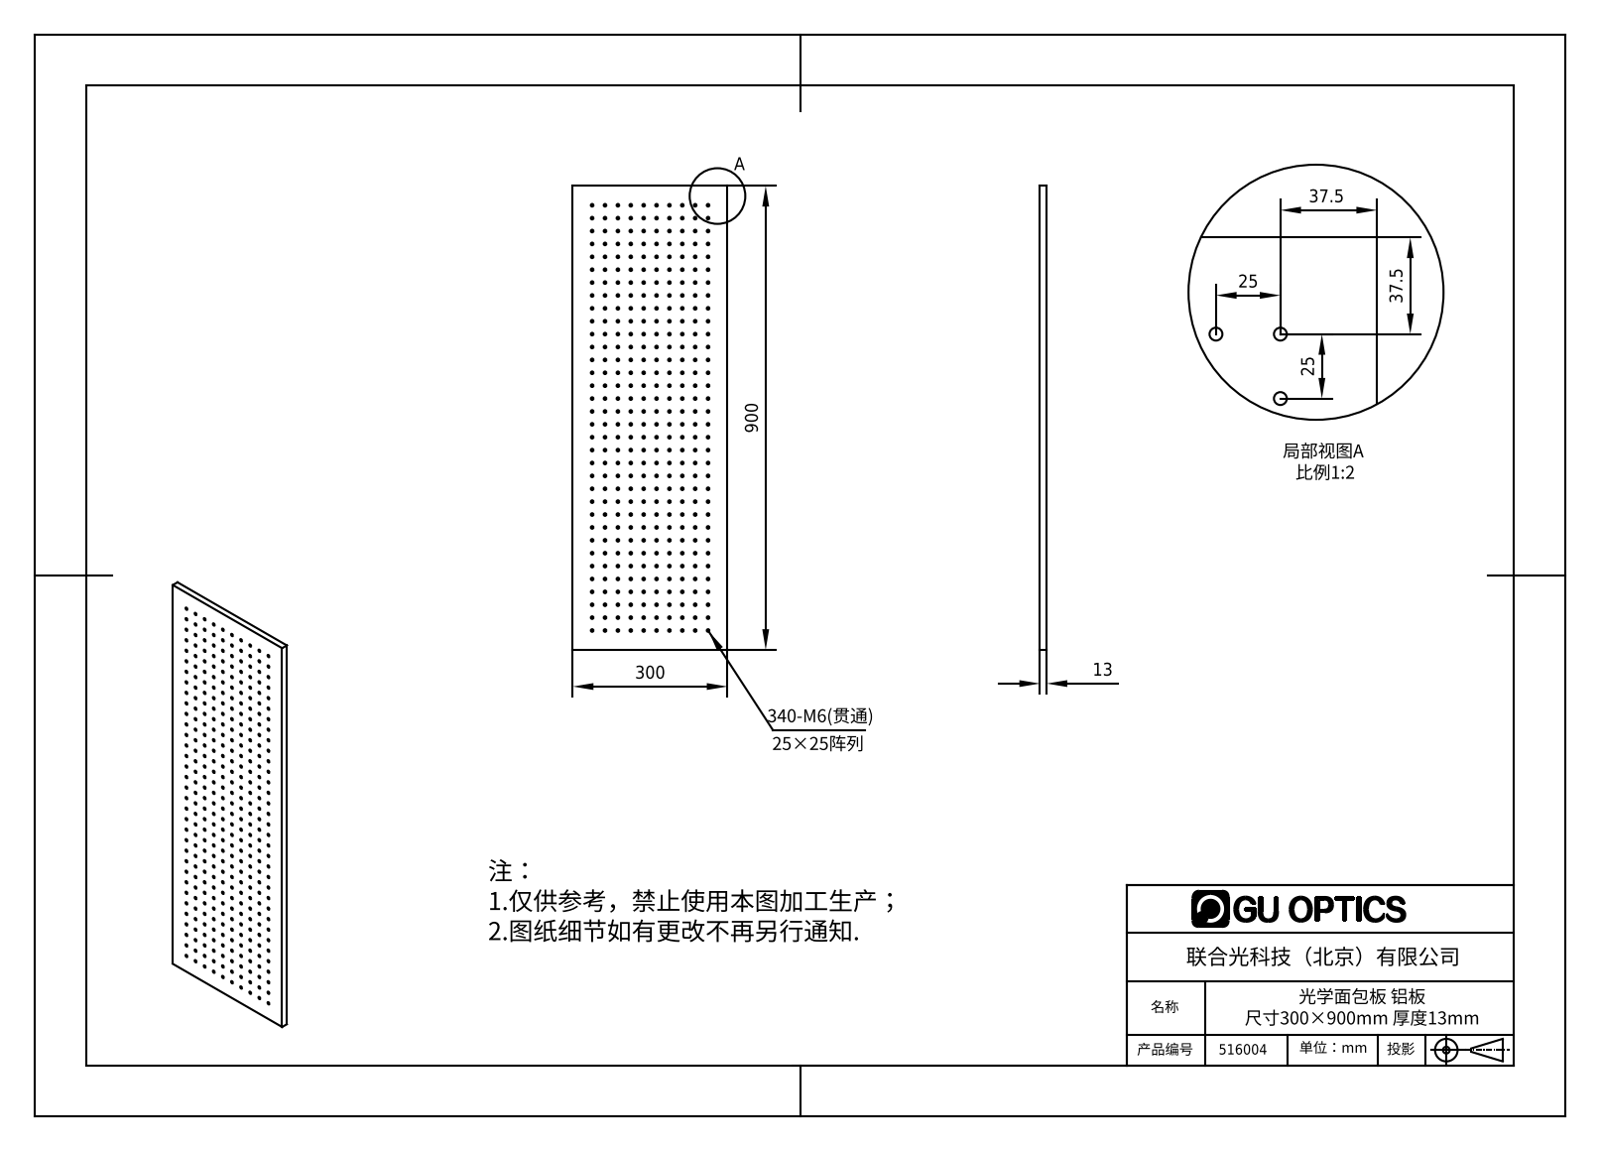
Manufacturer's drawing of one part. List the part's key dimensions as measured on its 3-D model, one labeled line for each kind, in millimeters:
Part name (STEP PRODUCT): 516004
STEP written by: SolidWorks 2016 (AUTOMOTIVE_DESIGN)
Units: millimetres
Bodies: 1 solid, 686 faces (6 planar, 680 cylindrical, 0 other)
Overall size (bounding box): 900 × 300 × 13
Volume: 3 423 000 mm³ · Surface area: 627 277 mm²
Round holes (diameter × count): ⌀5 ×340
Main face-to-face distances: 13, 300, 900
Hole centre spacings: 25, 50, 75, 100, 125, 150, 175, 200
